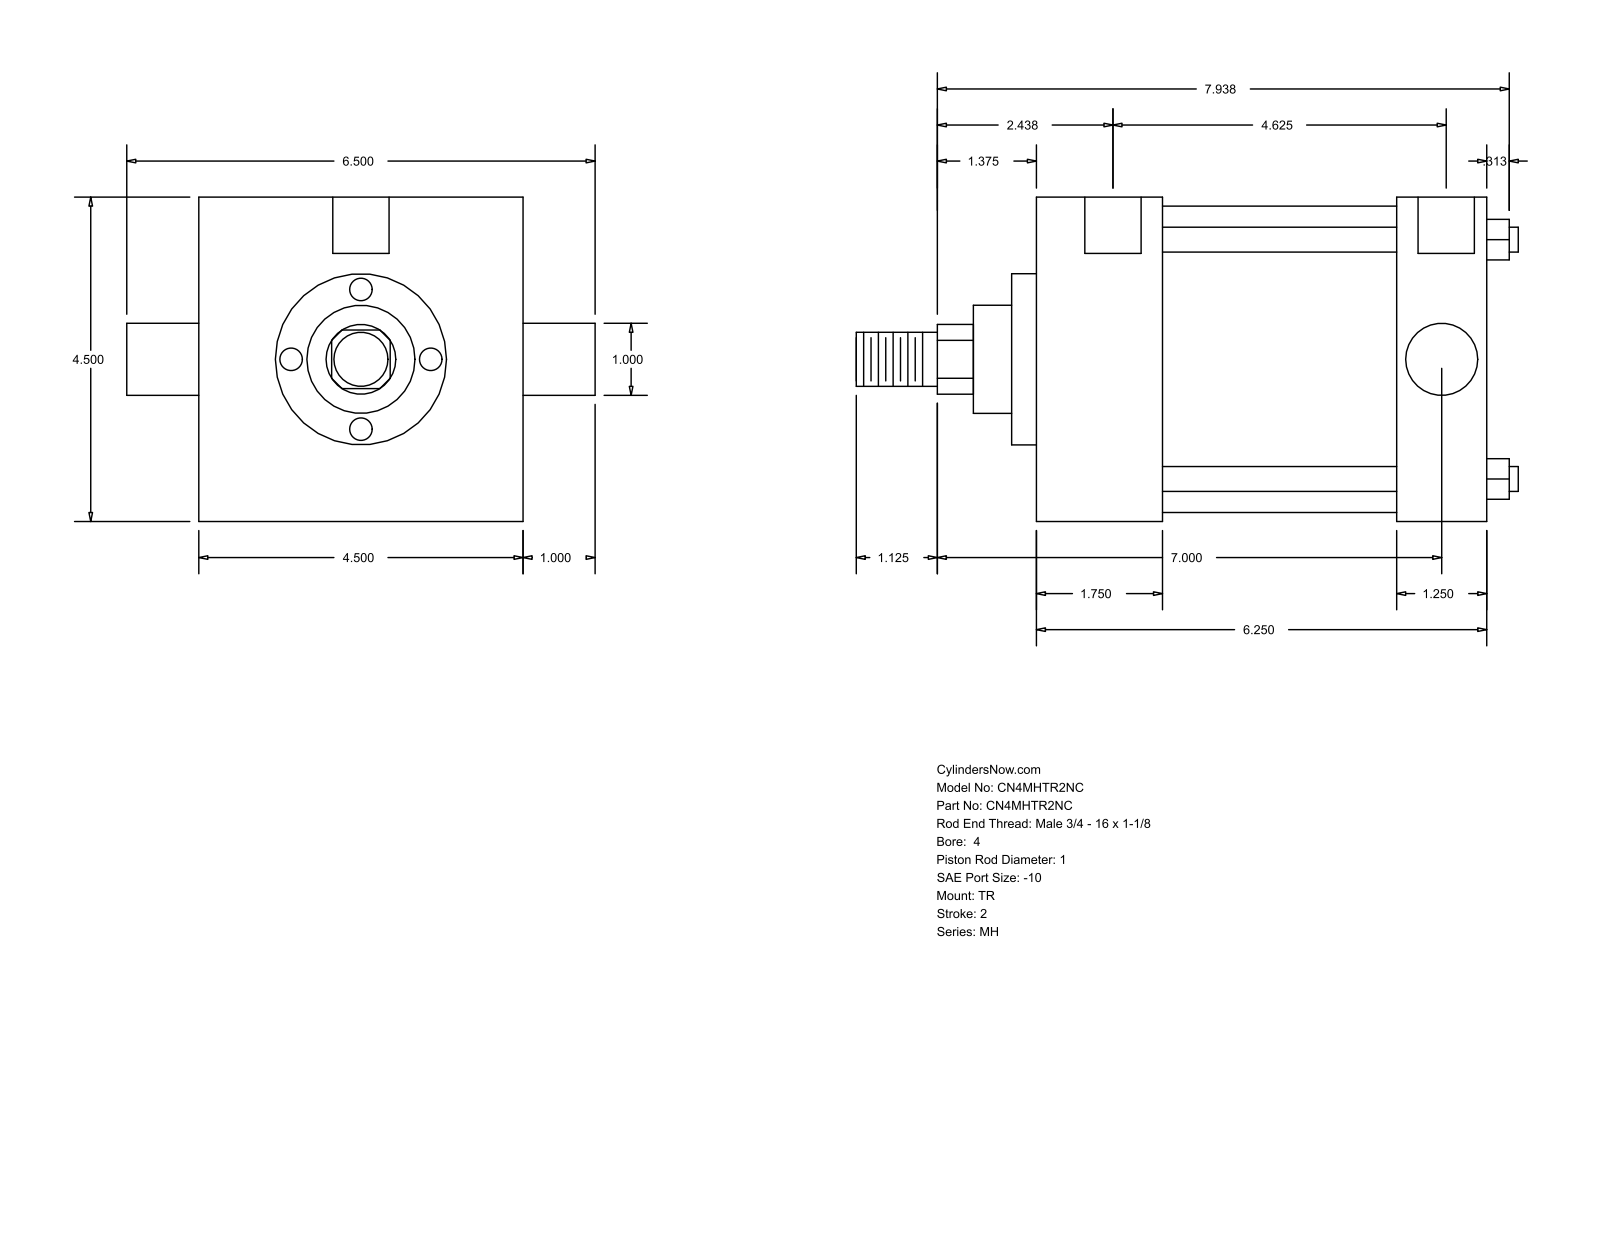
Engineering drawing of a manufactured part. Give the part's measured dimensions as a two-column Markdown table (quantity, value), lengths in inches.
| quantity | value |
| --- | --- |
| part name | MH_TR__0400_1 |
| STEP written by | GSSL Pune (CONFIG_CONTROL_DESIGN) |
| units | inches |
| bodies | 0 solids, 86 faces (61 planar, 25 cylindrical, 0 other) |
| overall size | 9.187 × 6.5 × 4.5 |
| round holes (diameter × count) | 0.344 × 3, 0.781 × 2 |
| round bosses / shafts (diameter × count) | 0.345 × 4, 1 × 2, 4.25 × 1, 2.375 × 1, 1.5 × 1, 0.75 × 1 |
| partial cylindrical surfaces (radius × count) | 0.484 × 1 |
| main face-to-face distances | 4.5, 6.25, 1.75, 5, 3.25, 1.25, 0.344, 2.094, 5.344, 6.594 |
| hole center spacings | 0.062, 4.687, 4.625, 4.75 |
